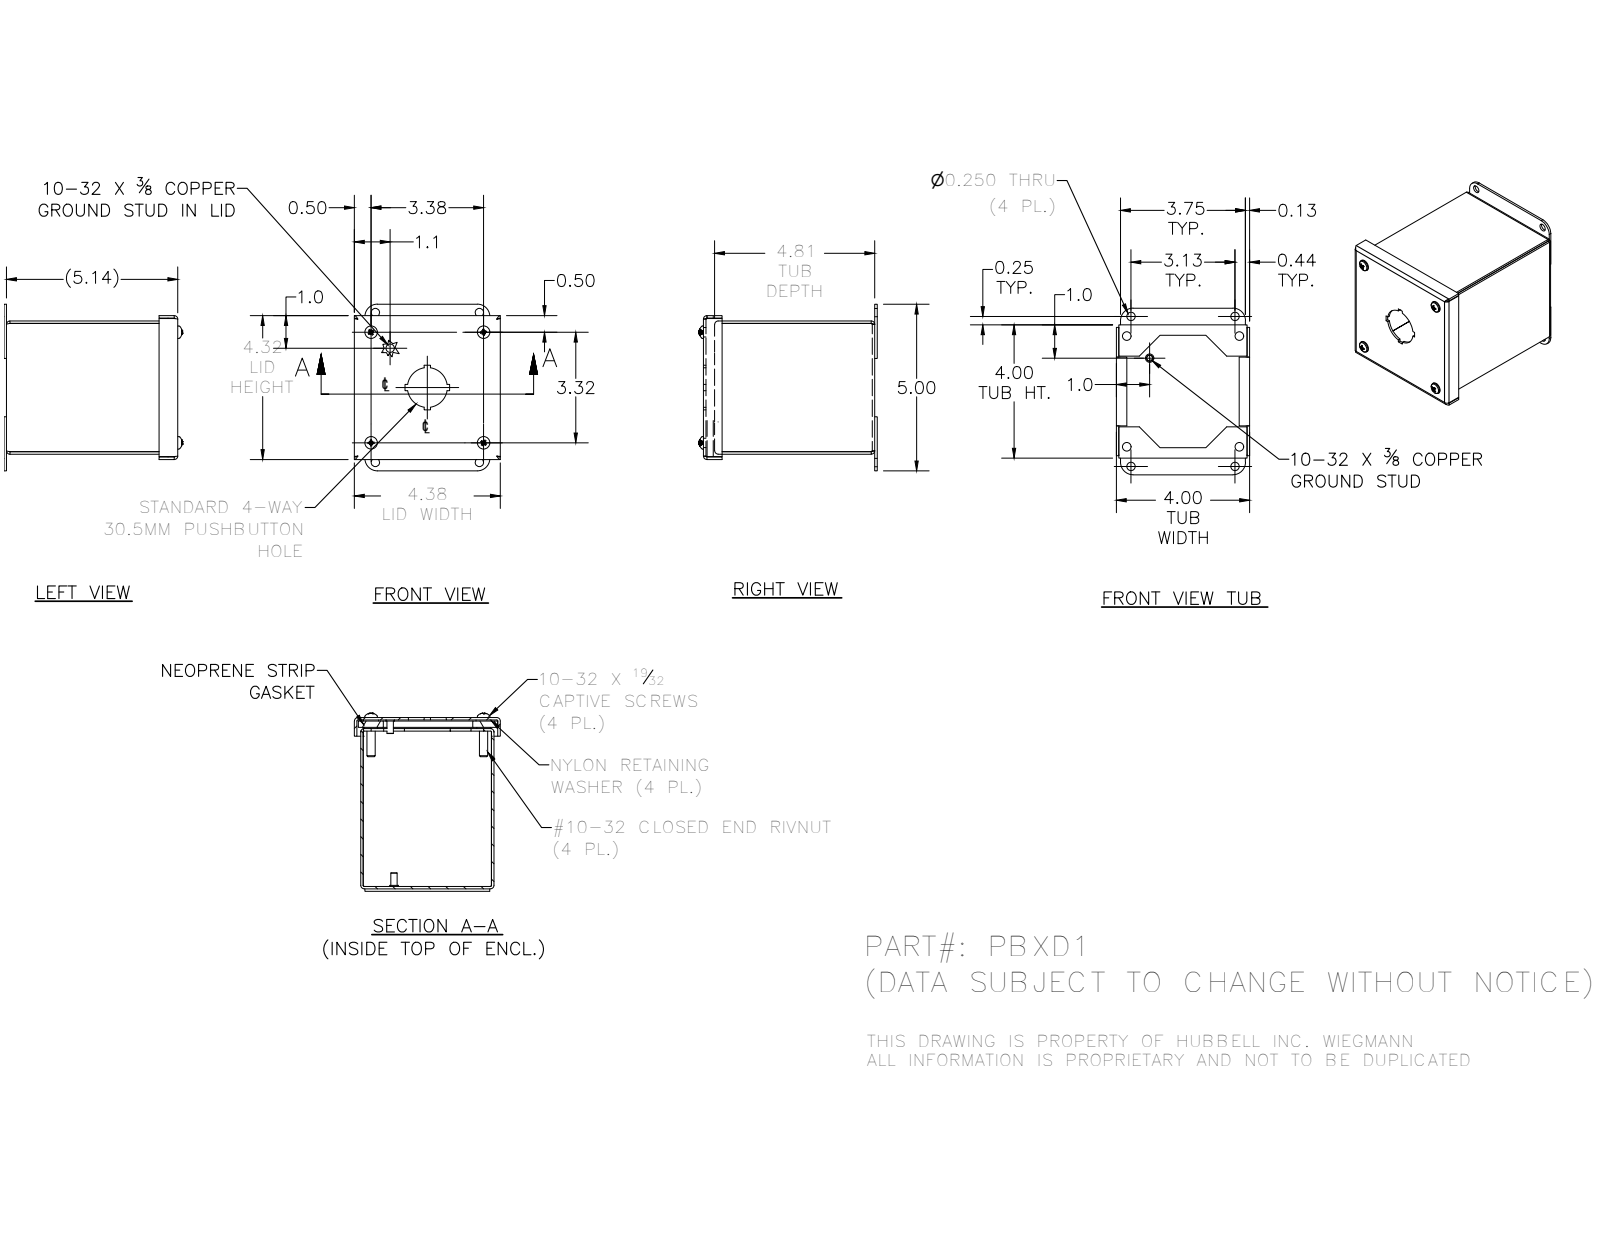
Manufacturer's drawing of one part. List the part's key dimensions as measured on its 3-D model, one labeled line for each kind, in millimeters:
Part name (STEP PRODUCT): PBXD1LID; 372163; 39077; PBXD1BKP (+5 more)
STEP written by: Autodesk Inventor 2016 (AUTOMOTIVE_DESIGN)
Units: millimetres
Bodies: 20 solids, 504 faces (290 planar, 100 cylindrical, 114 other)
Overall size (bounding box): 135.79 × 127 × 111.25
Volume: 192 975 mm³ · Surface area: 196 935 mm²
Round holes (diameter × count): ⌀3.96 ×4, ⌀4.98 ×4, ⌀6.35 ×4, ⌀6.53 ×4, ⌀7.06 ×4, ⌀7.14 ×4, ⌀7.95 ×4, ⌀30.48 ×1
Round bosses / shafts (diameter × count): ⌀4.83 ×6, ⌀11.51 ×4, ⌀10.31 ×4, ⌀9.47 ×4, ⌀6.3 ×4, ⌀6.35 ×2
Partial cylindrical surfaces — rounded edges, fillets, slot ends (radius × count): R0.79 ×12, R2.67 ×12, R2.27 ×4, R9.53 ×4
Main face-to-face distances: 1.88, 99.72, 101.6, 97.84, 128.73, 130.61, 126.85, 3.76, 132.49, 4.78
Hole centre spacings: 99.36, 15.33, 15.34, 60.16, 60.17, 69.58, 69.59, 79.39
